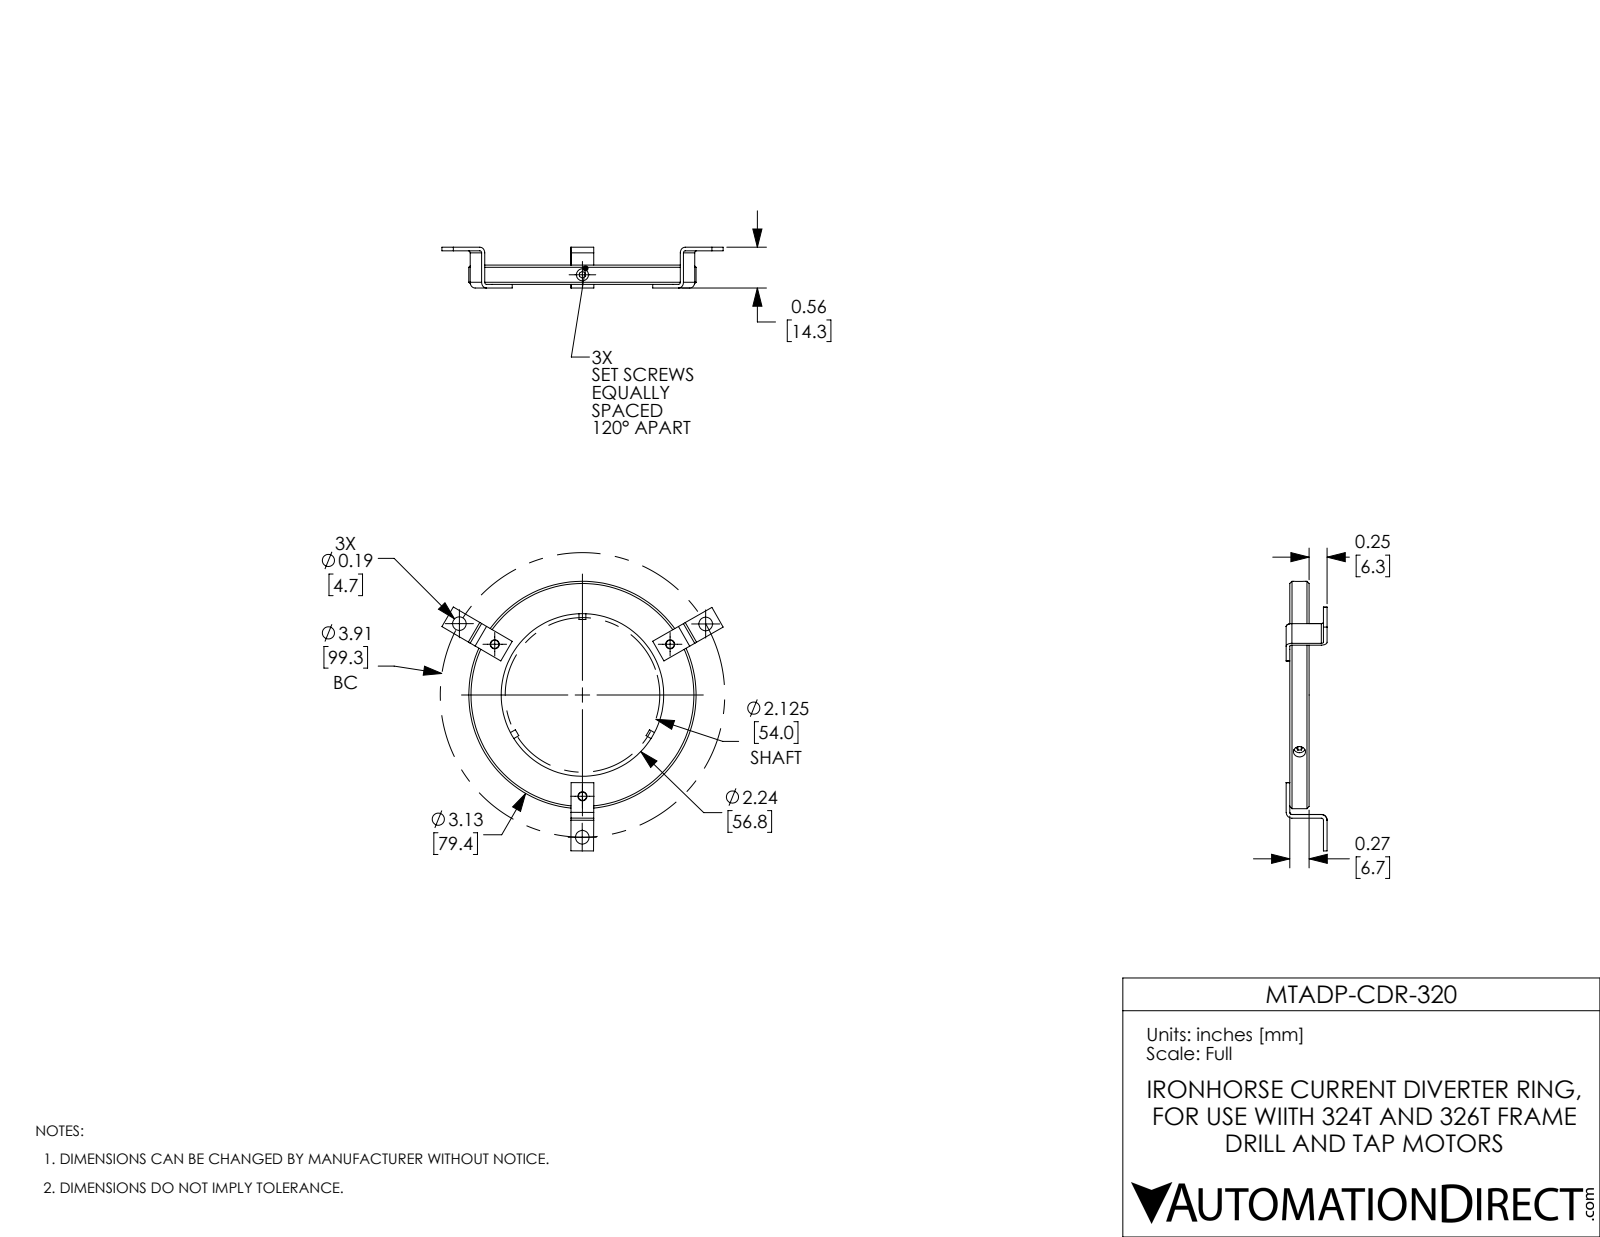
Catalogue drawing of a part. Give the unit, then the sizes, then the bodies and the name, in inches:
Units: inches
Overall size (bounding box): 3.867 × 3.706 × 0.562
Round holes (diameter × count): ⌀0.112 ×3, ⌀0.125 ×3, ⌀0.136 ×3, ⌀0.166 ×3, ⌀0.187 ×3, ⌀2.235 ×1
Round bosses / shafts (diameter × count): ⌀0.094 ×3, ⌀3.125 ×1
Partial cylindrical surfaces — rounded edges, fillets, slot ends (radius × count): R0.029 ×6, R0.079 ×6
Main face-to-face distances: 0.265, 0.05, 0.512, 0.315, 0.197, 0.462, 0.247, 0.562, 0.312, 0.081
Hole centre spacings: 1.393, 1.956, 2.412, 3.387, 0.563, 2.912, 2.914, 0.563
Volume: 1.024 in³ · Surface area: 15.57 in²
Bodies: 6 solids, 126 faces (65 planar, 52 cylindrical, 9 other)
Part name (STEP PRODUCT): 1839-A-M0020-0 R1 minus hex heads 1 Ext1 P1 Coord
STEP written by: SolidWorks 2017 (AUTOMOTIVE_DESIGN)
